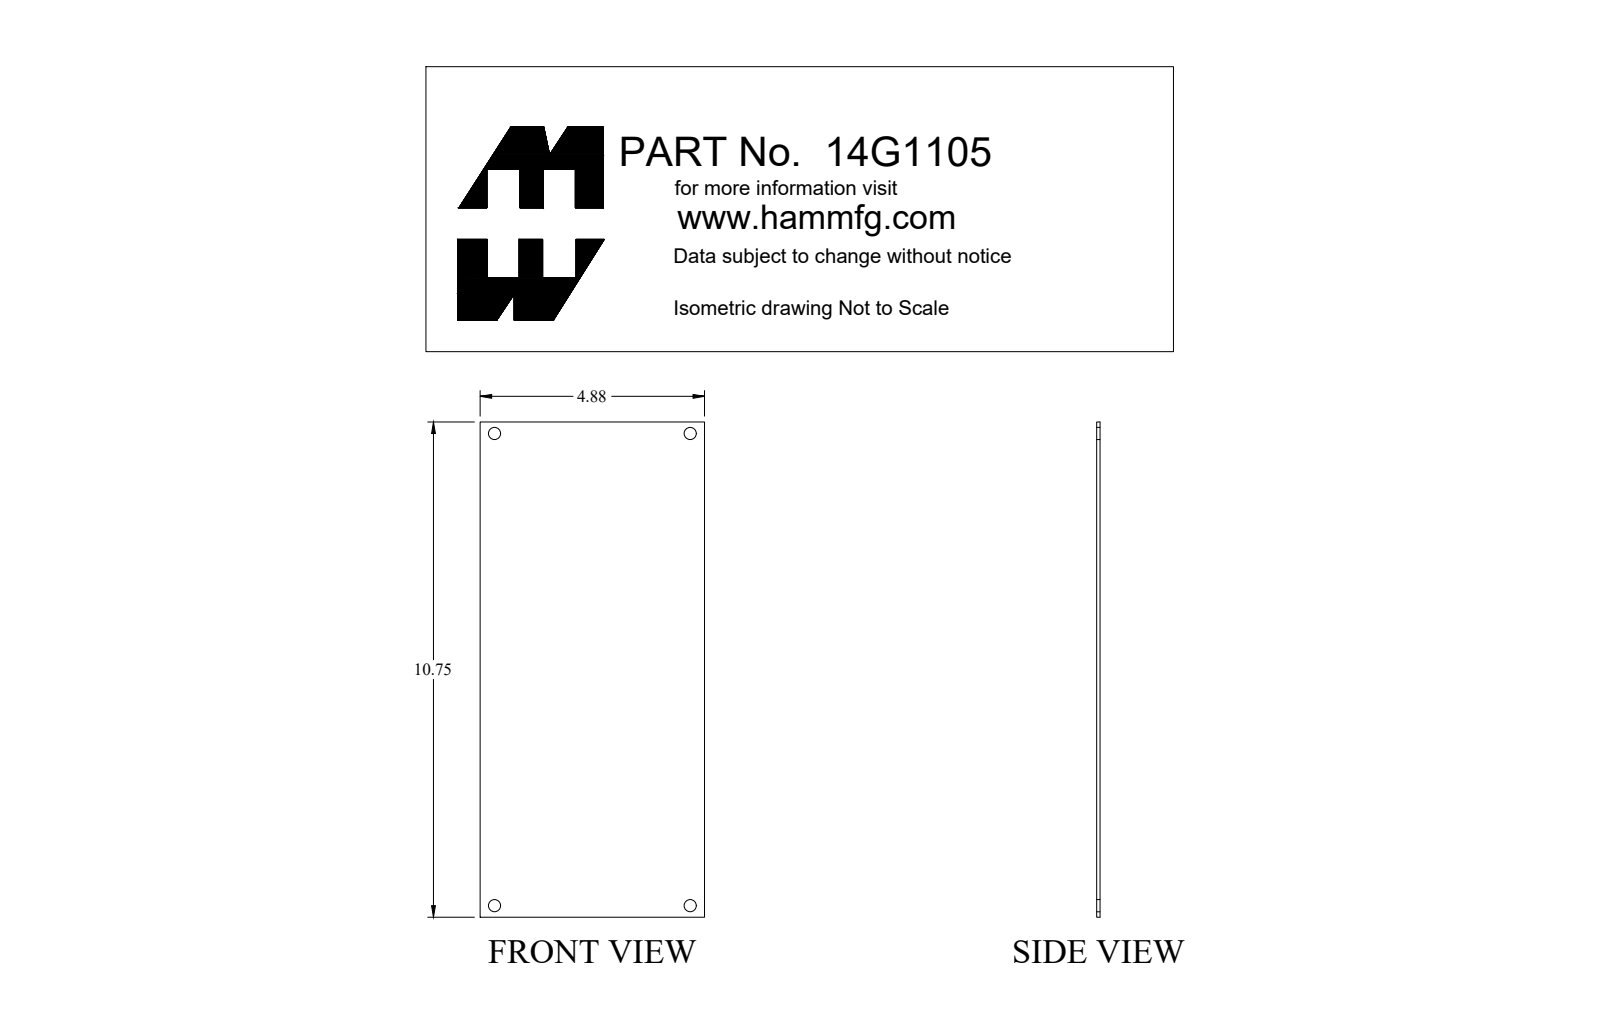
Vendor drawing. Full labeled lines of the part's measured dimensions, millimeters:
Part name (STEP PRODUCT): 14G1105
STEP written by: SolidWorks 2018 (AUTOMOTIVE_DESIGN)
Units: millimetres
Bodies: 1 solid, 10 faces (6 planar, 4 cylindrical, 0 other)
Overall size (bounding box): 273.1 × 123.8 × 1.8
Volume: 61 570 mm³ · Surface area: 68 970 mm²
Round holes (diameter × count): ⌀6.7 ×4
Main face-to-face distances: 1.8, 123.8, 273.1
Hole centre spacings: 108, 260.4, 281.8
